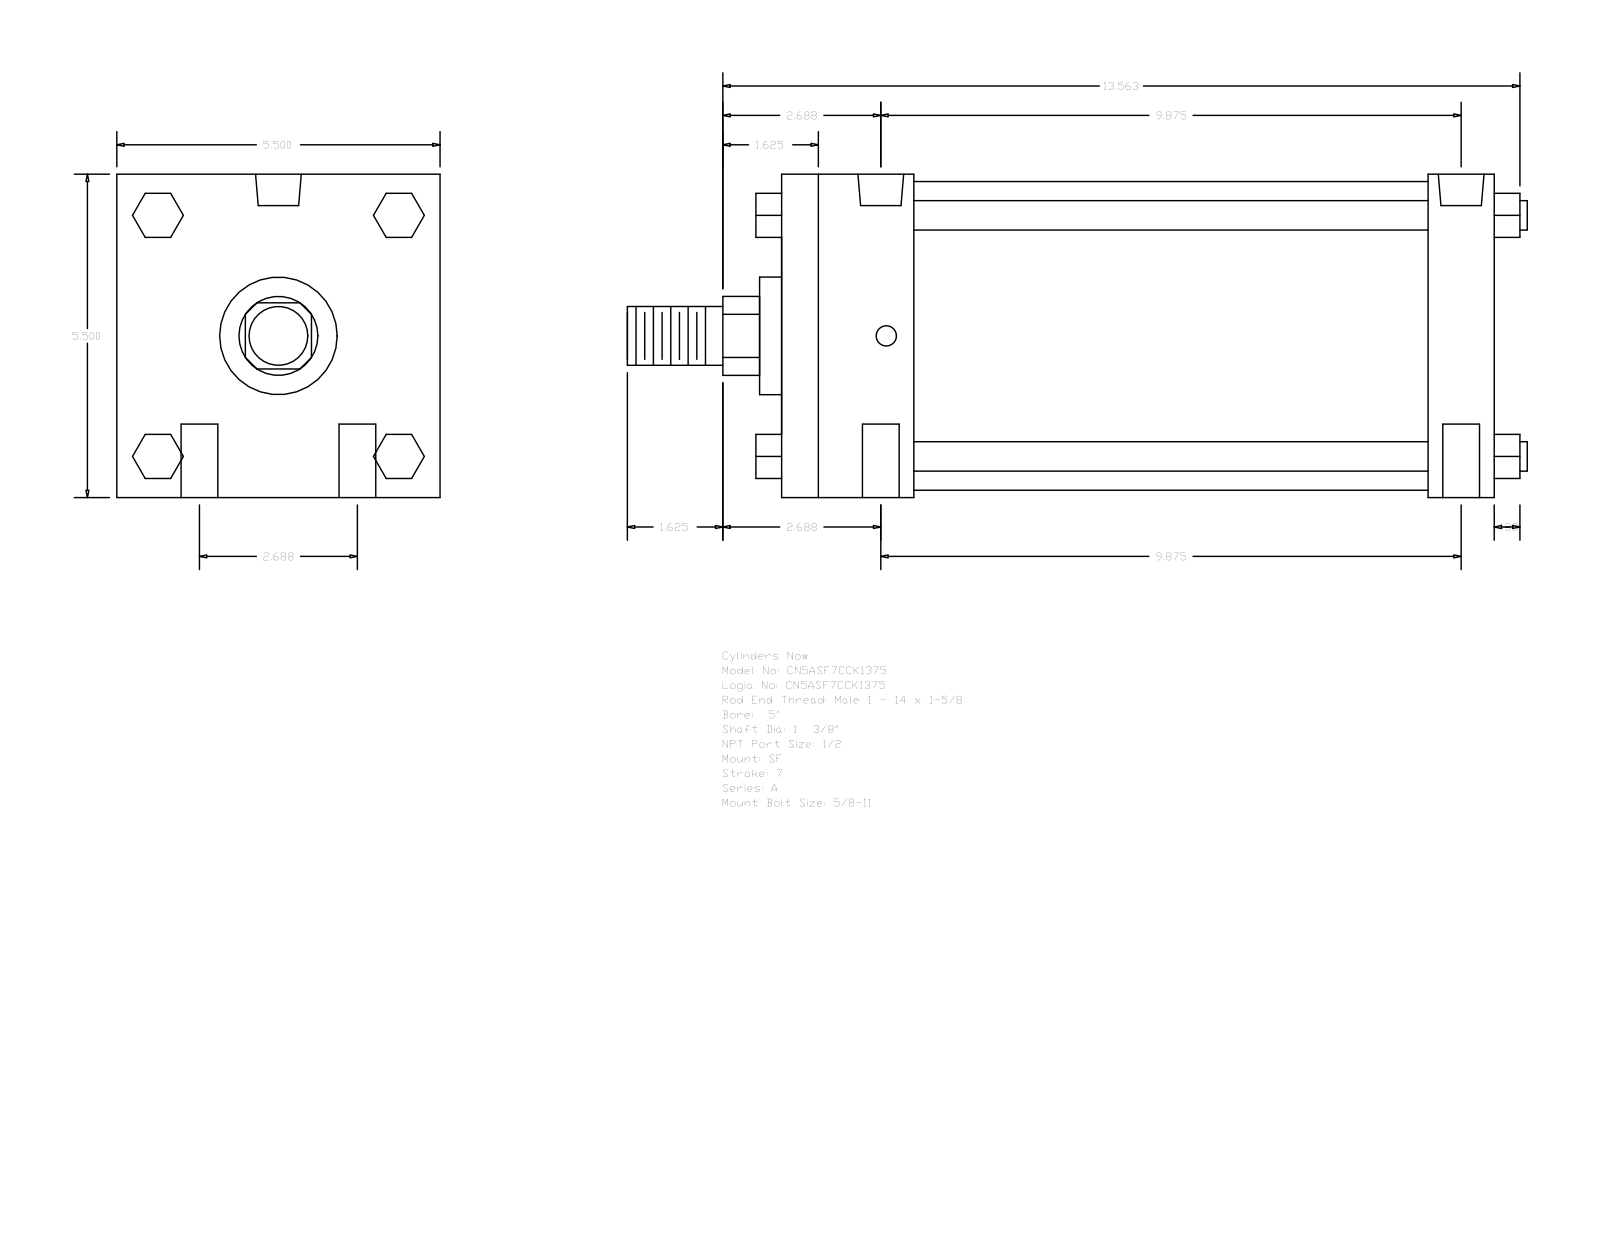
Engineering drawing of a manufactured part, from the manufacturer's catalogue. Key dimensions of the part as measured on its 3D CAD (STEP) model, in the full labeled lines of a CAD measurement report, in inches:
Part name (STEP PRODUCT): A_SF__0500_1.375
STEP written by: GSSL Pune (CONFIG_CONTROL_DESIGN)
Units: inches
Bodies: 0 solids, 124 faces (94 planar, 30 cylindrical, 0 other)
Overall size (bounding box): 15.313 × 5.5 × 5.5
Round holes (diameter × count): ⌀0.625 ×4, ⌀0.344 ×2, ⌀0.778 ×2
Round bosses / shafts (diameter × count): ⌀0.5 ×4, ⌀5.25 ×1, ⌀2 ×1, ⌀1.375 ×1, ⌀1 ×1
Partial cylindrical surfaces — rounded edges, fillets, slot ends (radius × count): R0.672 ×1
Main face-to-face distances: 5.5, 12.125, 2.25, 1.125, 11, 8.75, 9.875, 0.75, 2.05, 3.55
Hole centre spacings: 1.344, 9.966, 9.875, 2.687, 10.234, 9.687
